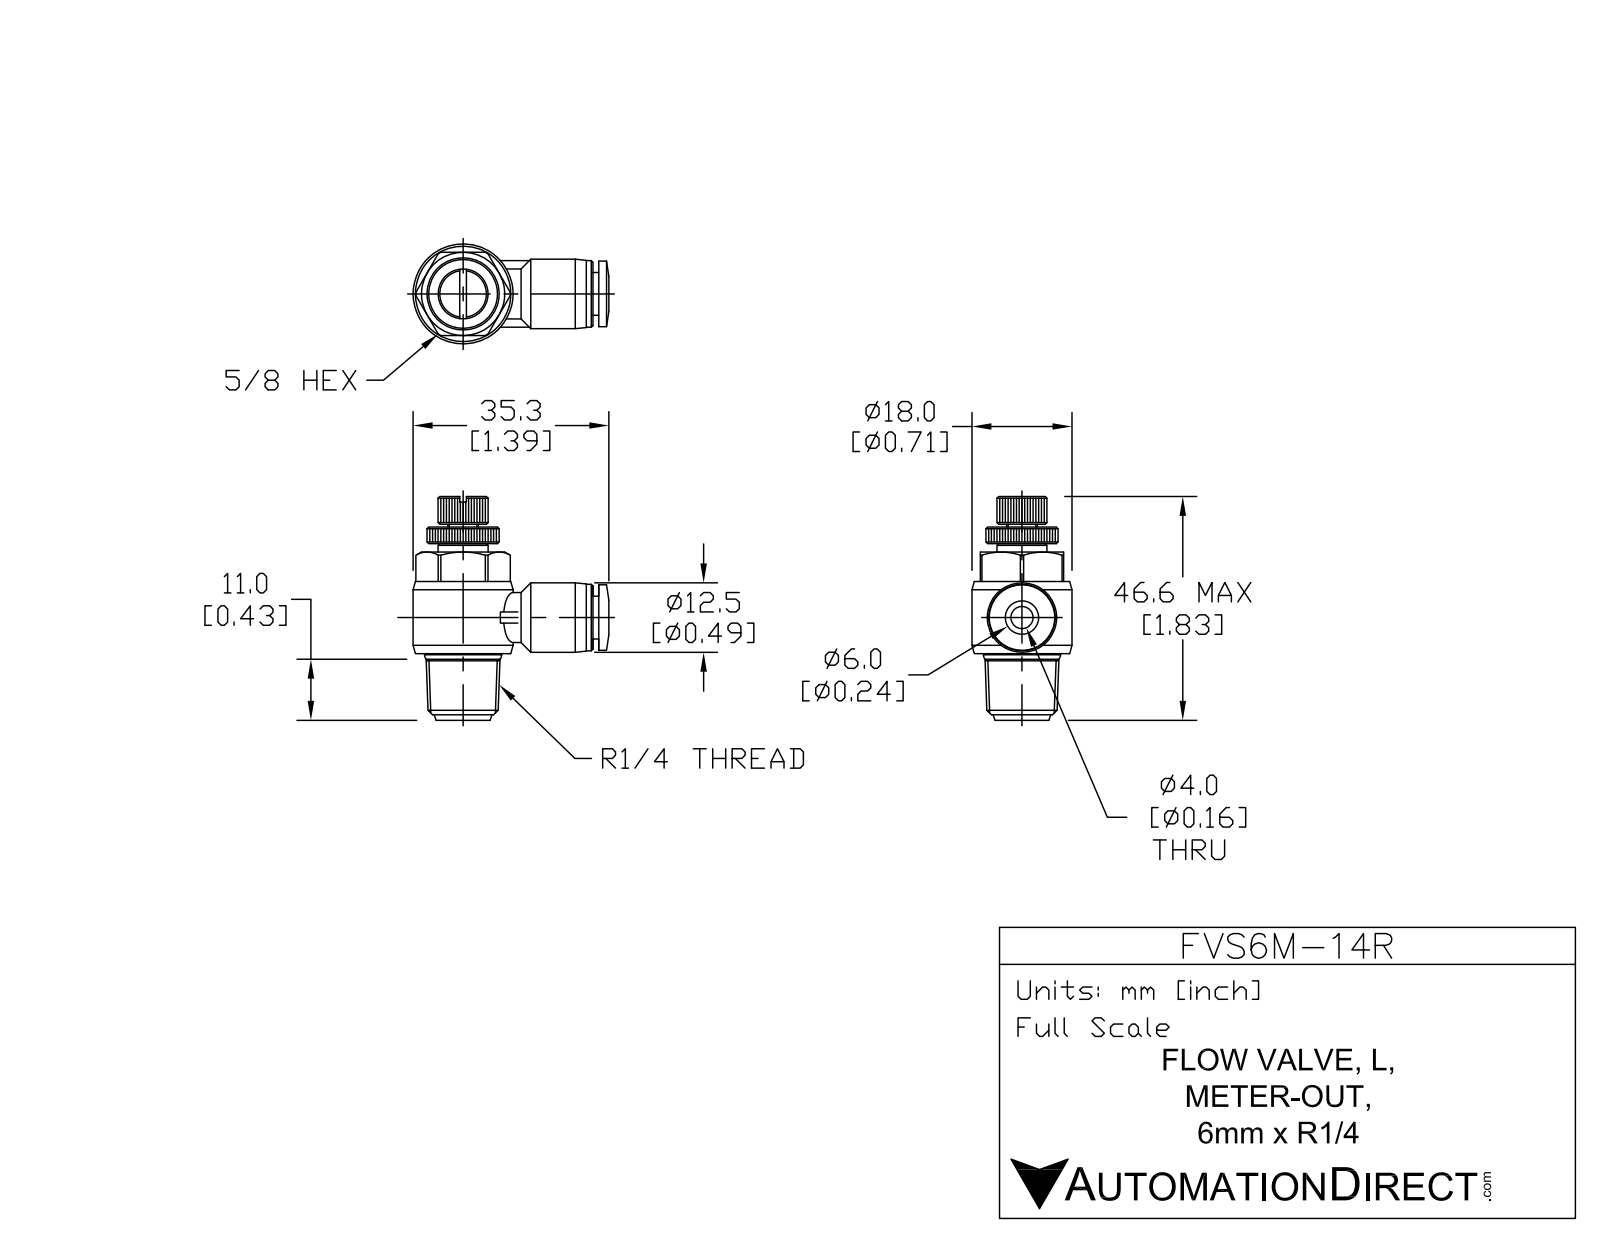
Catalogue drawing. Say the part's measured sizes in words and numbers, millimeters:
The part is named "FVS6M-14R". Its 3-D file was written by "SolidWorks 2015 (AUTOMOTIVE_DESIGN)". It is 1 solid with 417 faces: 187 planar, 110 cylindrical and 120 other. Overall it measures 46.6 by 35.3 by 18 millimeters. Its volume is 7 600 cubic millimeters and its surface area 4 134 square millimeters. Round holes: 2 of diameter 4.5, 1 of diameter 6.3. Round bosses or shafts: 2 of diameter 9, 1 of diameter 18, 1 of diameter 13.4, 1 of diameter 12.5, 1 of diameter 12, 1 of diameter 11.8, 1 of diameter 7.7, 1 of diameter 5.5. Partial cylindrical surfaces (rounded edges, fillets, slot ends): 1 of radius 6.5, 1 of radius 8.5. The main face-to-face distances are 15, 4.5, 17.8, 22.3, 1.5, 29.8, 12, 19.3, 3, 31.3.
